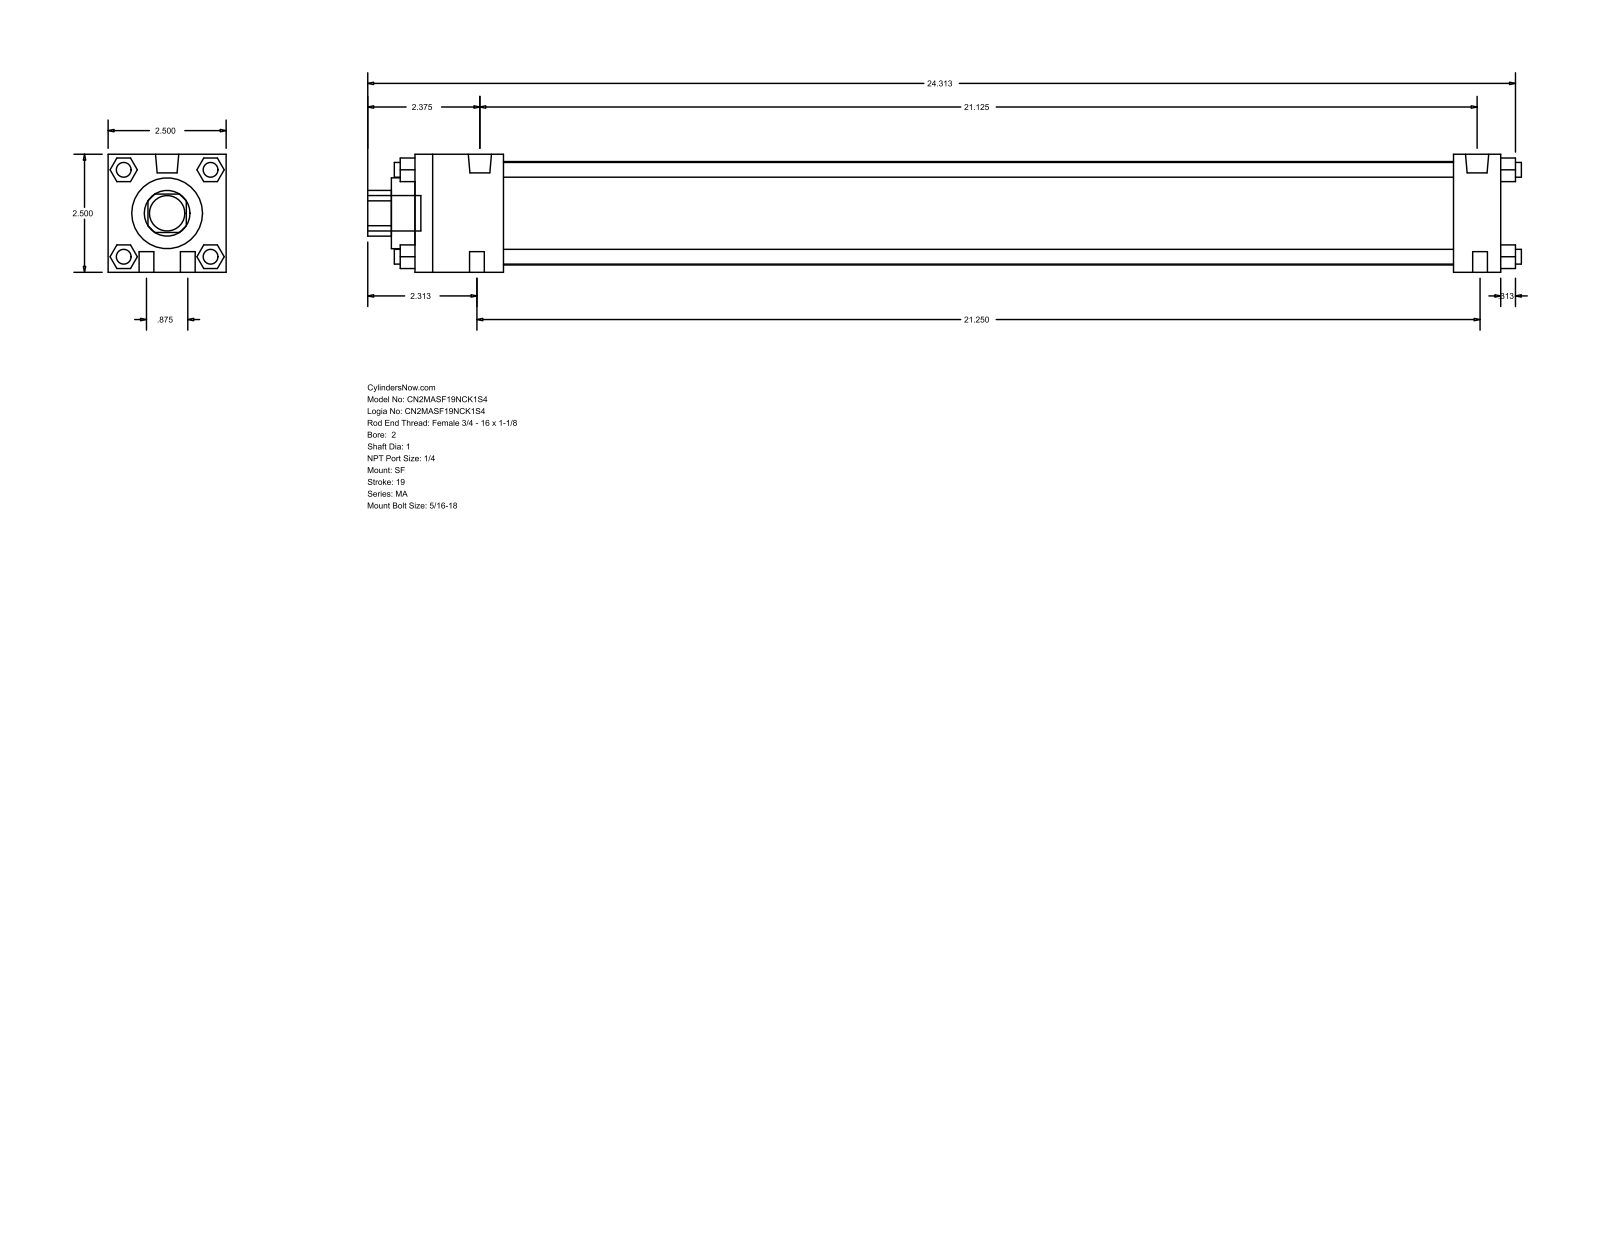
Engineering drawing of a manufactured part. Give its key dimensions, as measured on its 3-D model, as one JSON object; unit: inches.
{"part_name": "MA_SF__0200_1", "step_written_by": "GSSL Pune (CONFIG_CONTROL_DESIGN)", "units": "inches", "bodies": {"solids": 0, "faces": 124, "planar": 94, "cylindrical": 30, "other": 0}, "overall_size": [24.437, 2.5, 2.5], "round_holes": [[1, 1], [1.5, 1], [2.19, 1]], "round_bosses_or_shafts": [[0.313, 10], [0.492, 2], [0.75, 1]], "partial_cylinders_radius": [[0.484, 1]], "face_to_face_distances": [2.5, 23, 0.5, 1, 22, 1.875, 20.125, 21.125, 0.92, 1.593]}
